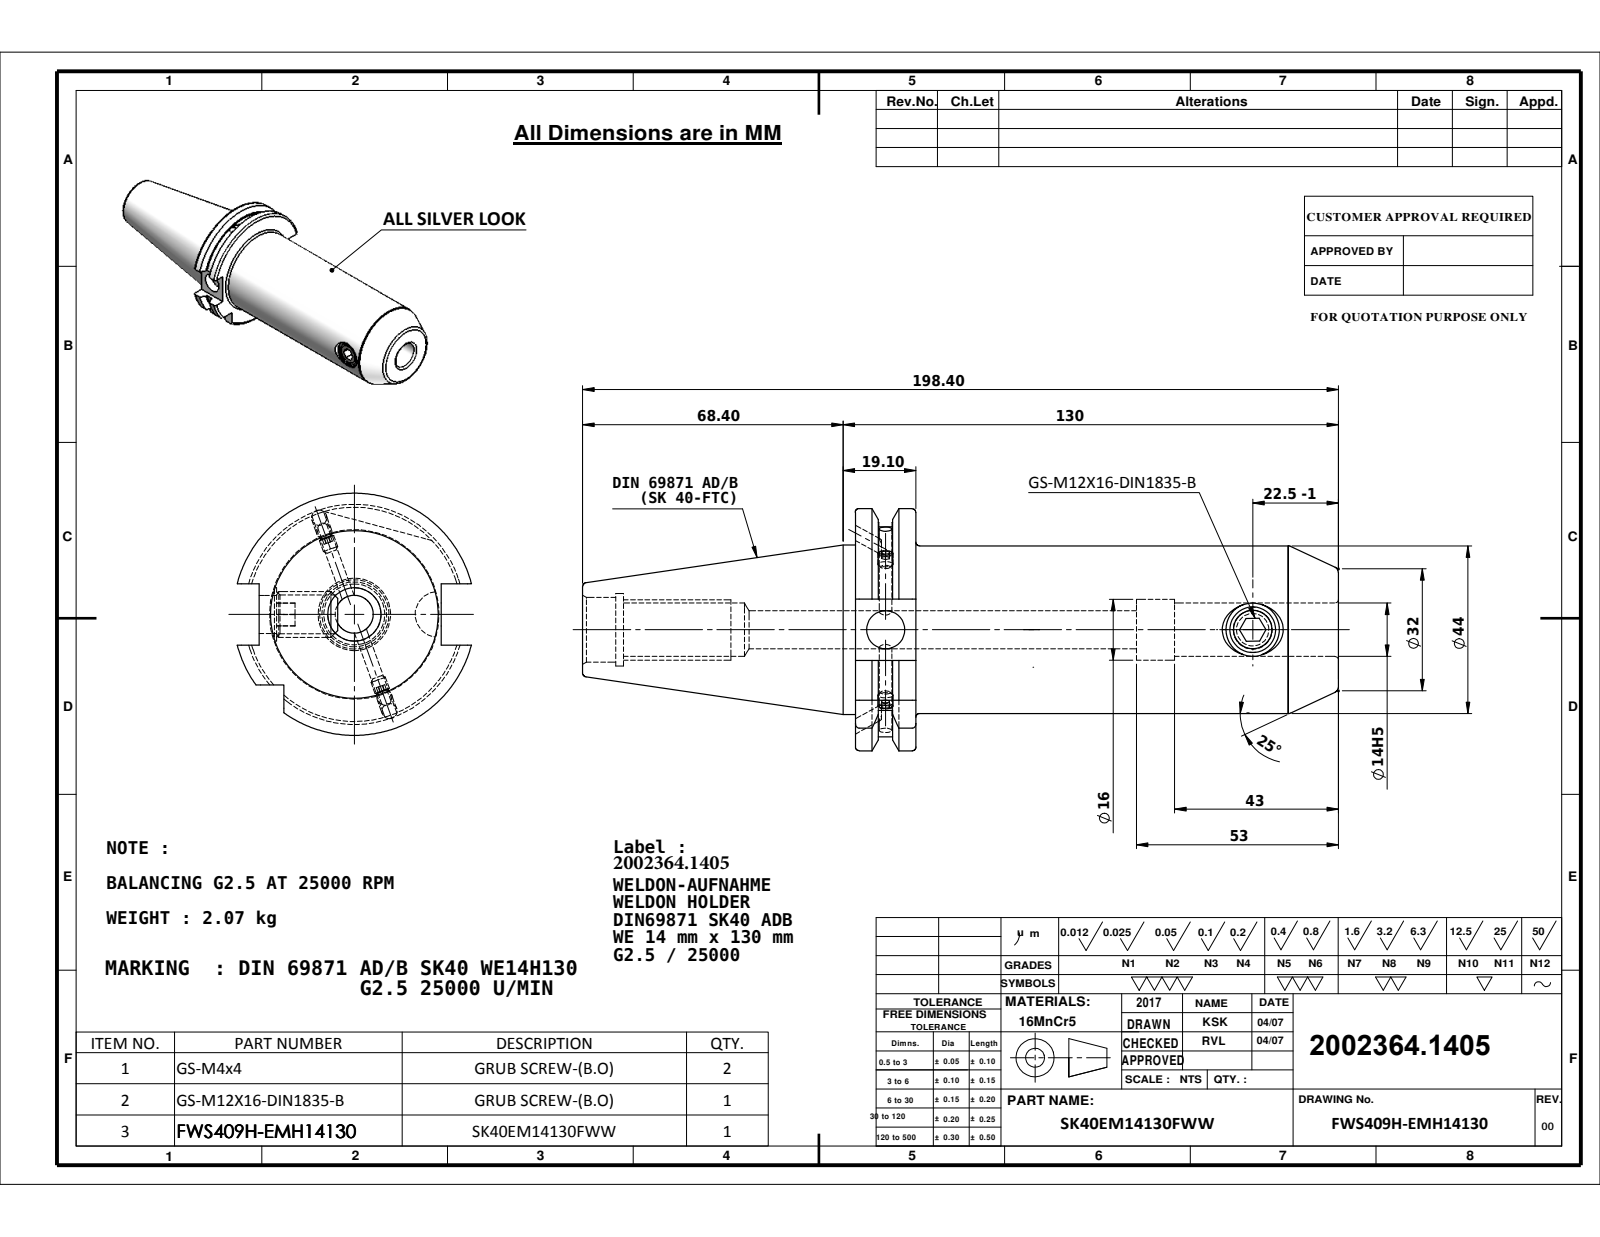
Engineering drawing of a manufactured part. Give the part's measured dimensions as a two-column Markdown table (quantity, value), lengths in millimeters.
| quantity | value |
| --- | --- |
| part name | M4X4_DIN 913 - M4 x 4-N; SK40EM14130FWW; M12X16._ISO 4026 - M12 x 12-N; 91406-WE714130 |
| STEP written by | SolidWorks 2009 (CONFIG_CONTROL_DESIGN) |
| units | millimeters |
| bodies | 4 solids, 160 faces (58 planar, 44 cylindrical, 58 other) |
| overall size | 198.4 × 63.55 × 61.48 |
| volume | 252 111 mm³ |
| surface area | 41 033 mm² |
| round holes (diameter × count) | 10 × 2, 14 × 2, 3.3 × 1, 10.2 × 1, 16 × 1, 17 × 1, 19 × 1 |
| round bosses / shafts (diameter × count) | 4 × 2, 44.45 × 1, 44 × 1, 12 × 1 |
| partial cylindrical surfaces (radius × count) | 28.12 × 1, 31.77 × 1 |
| main face-to-face distances | 15.9, 126.8, 110.9, 16.1, 47.8, 4.6, 43.2, 71.6, 87.5, 198.4 |
| hole center spacings | 96.35 |
